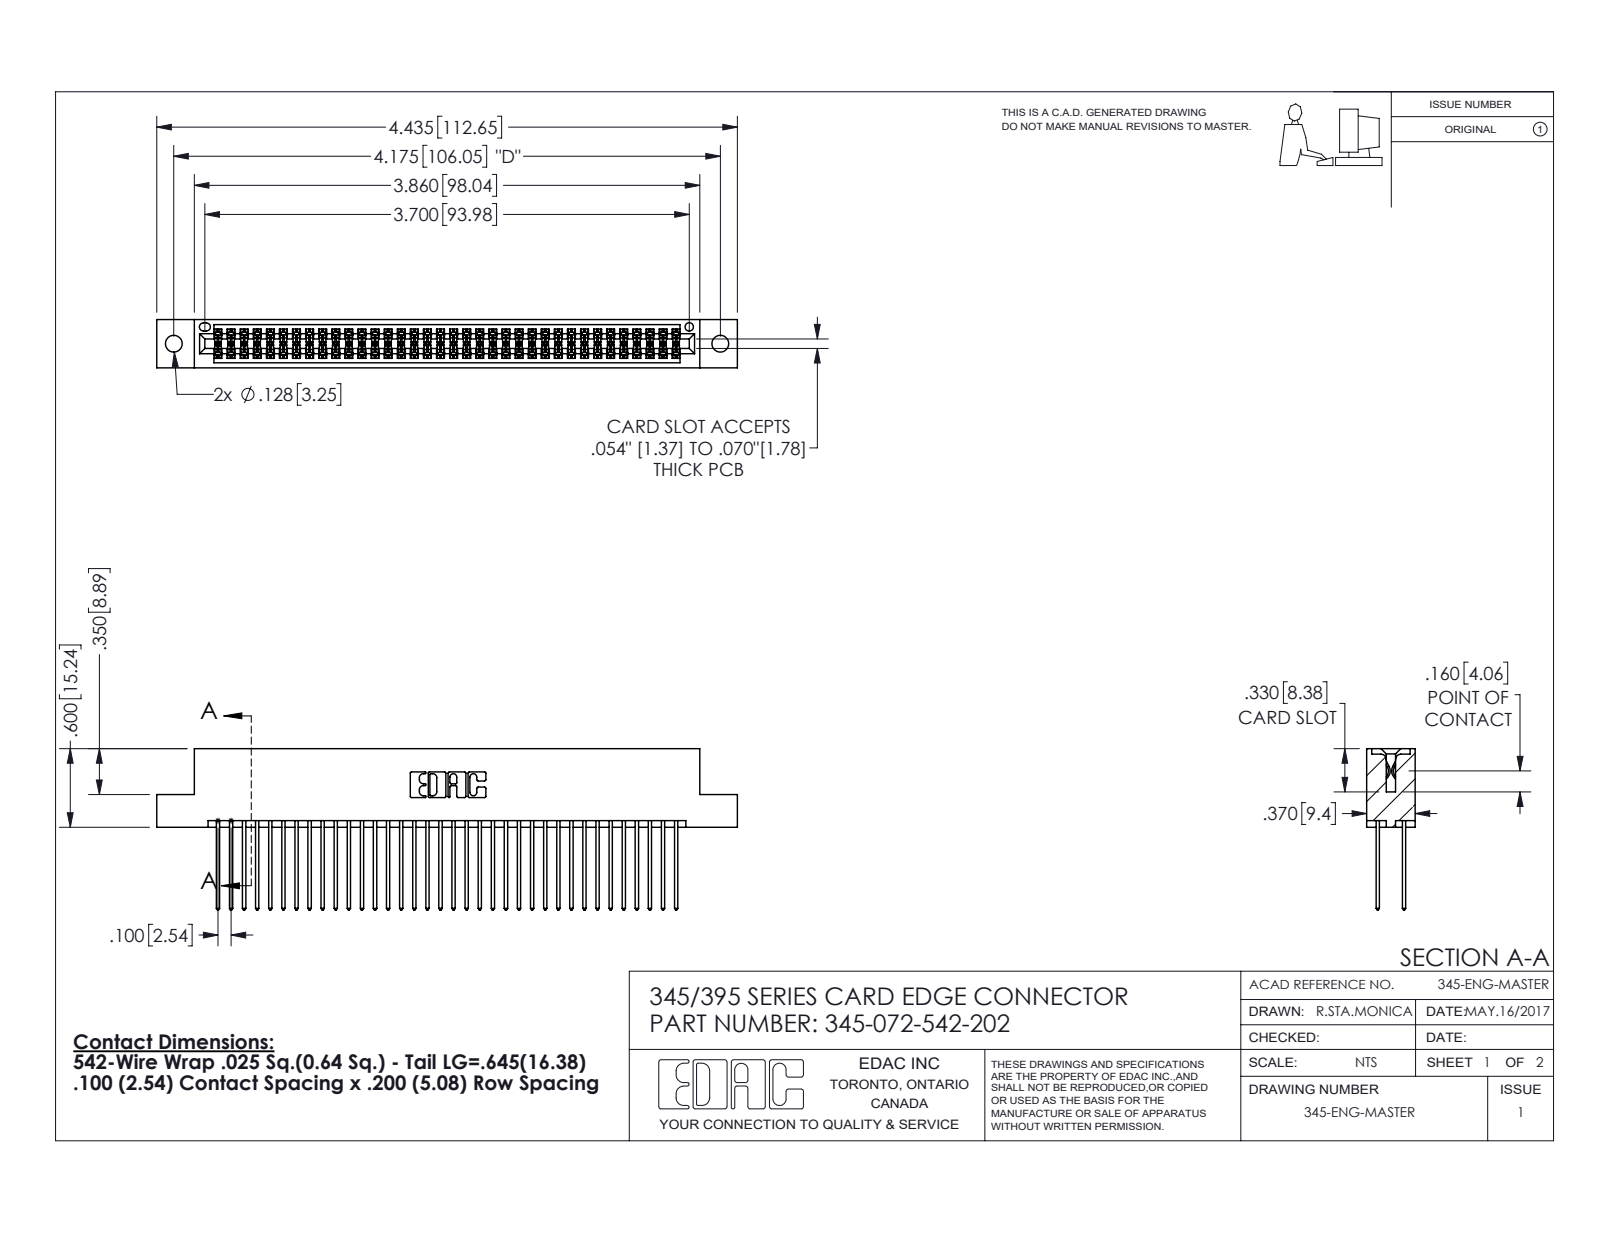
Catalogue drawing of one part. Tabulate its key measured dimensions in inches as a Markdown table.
| quantity | value |
| --- | --- |
| part name | 345-292-001_345-293-142; 345 Part_Flush Mounting Lugs - 0.128 Dia; 345-072-542-202 |
| STEP written by | SolidWorks 2016 (CONFIG_CONTROL_DESIGN) |
| units | inches |
| bodies | 73 solids, 3726 faces (2456 planar, 1270 cylindrical, 0 other) |
| overall size | 4.435 × 1.232 × 0.37 |
| volume | 0.683 in³ |
| surface area | 27.46 in² |
| round holes (diameter × count) | 0.128 × 2, 0.064 × 1 |
| partial cylindrical surfaces (radius × count) | 0.006 × 108, 0.01 × 72, 0.01 × 22, 0.007 × 6, 0.031 × 6, 0.026 × 3, 0.014 × 2, 0.019 × 2 |
| main face-to-face distances | 0.298, 0.072, 0.2, 0.098, 0.272, 0.025, 0.37, 0.225, 0.175, 0.149 |
| hole center spacings | 0.27, 3.939, 4.175 |
